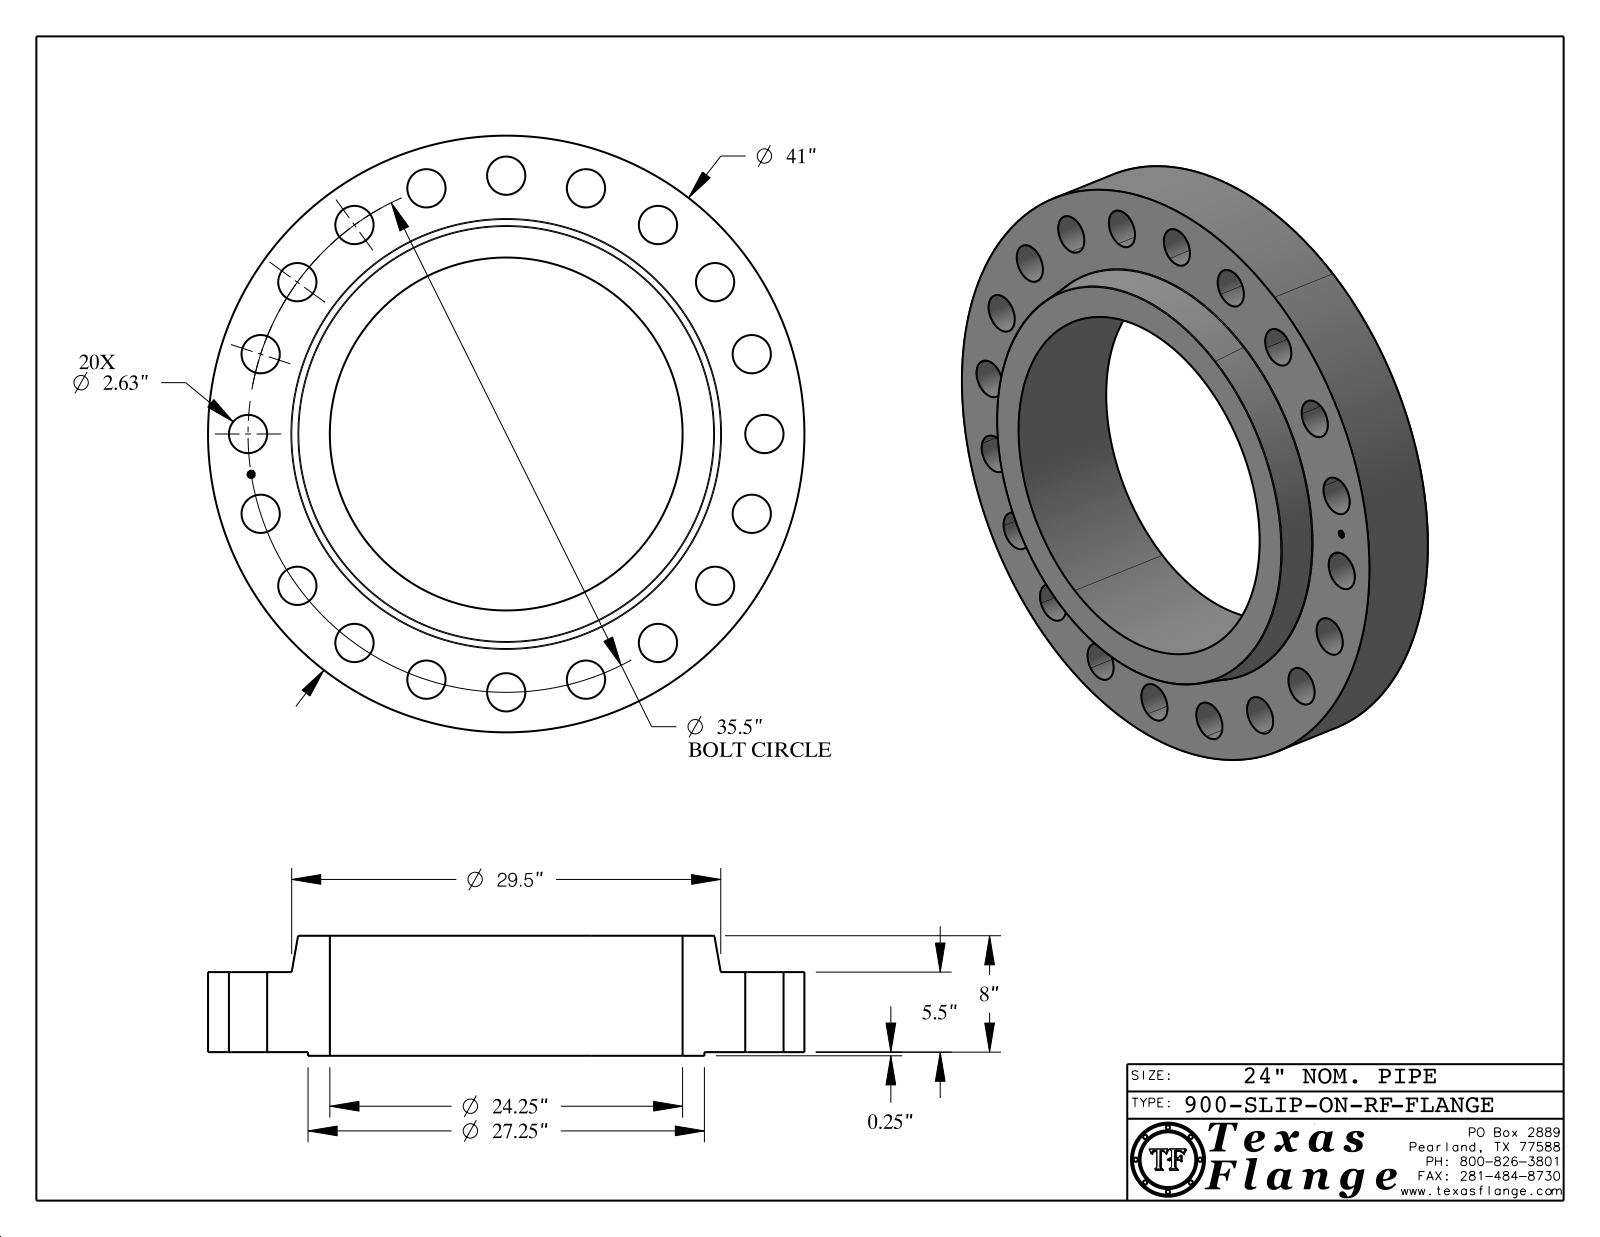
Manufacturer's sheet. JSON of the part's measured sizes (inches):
{"part_name": "900-SLIP-ON-RF", "step_written_by": "CATIA V5 STEP AP214 (AUTOMOTIVE_DESIGN)", "units": "inches", "bodies": {"solids": 1, "faces": 441, "planar": 369, "cylindrical": 66, "other": 6}, "overall_size": [41, 41, 8.25], "volume_in3": 4657, "surface_area_in2": 3955, "round_holes": [[2.63, 20], [0.495, 1], [24.25, 1]], "round_bosses_or_shafts": [[0.03, 8], [41, 1], [27.25, 1], [0.39, 1]], "face_to_face_distances": [5.5, 8, 2.5, 0.25, 5.75, 8.25, 5.735, 5.485, 0.015, 2.515], "hole_center_spacings": [17.75, 10.97, 28.72, 31.631, 16.117, 20.866, 25.102, 33.762]}
